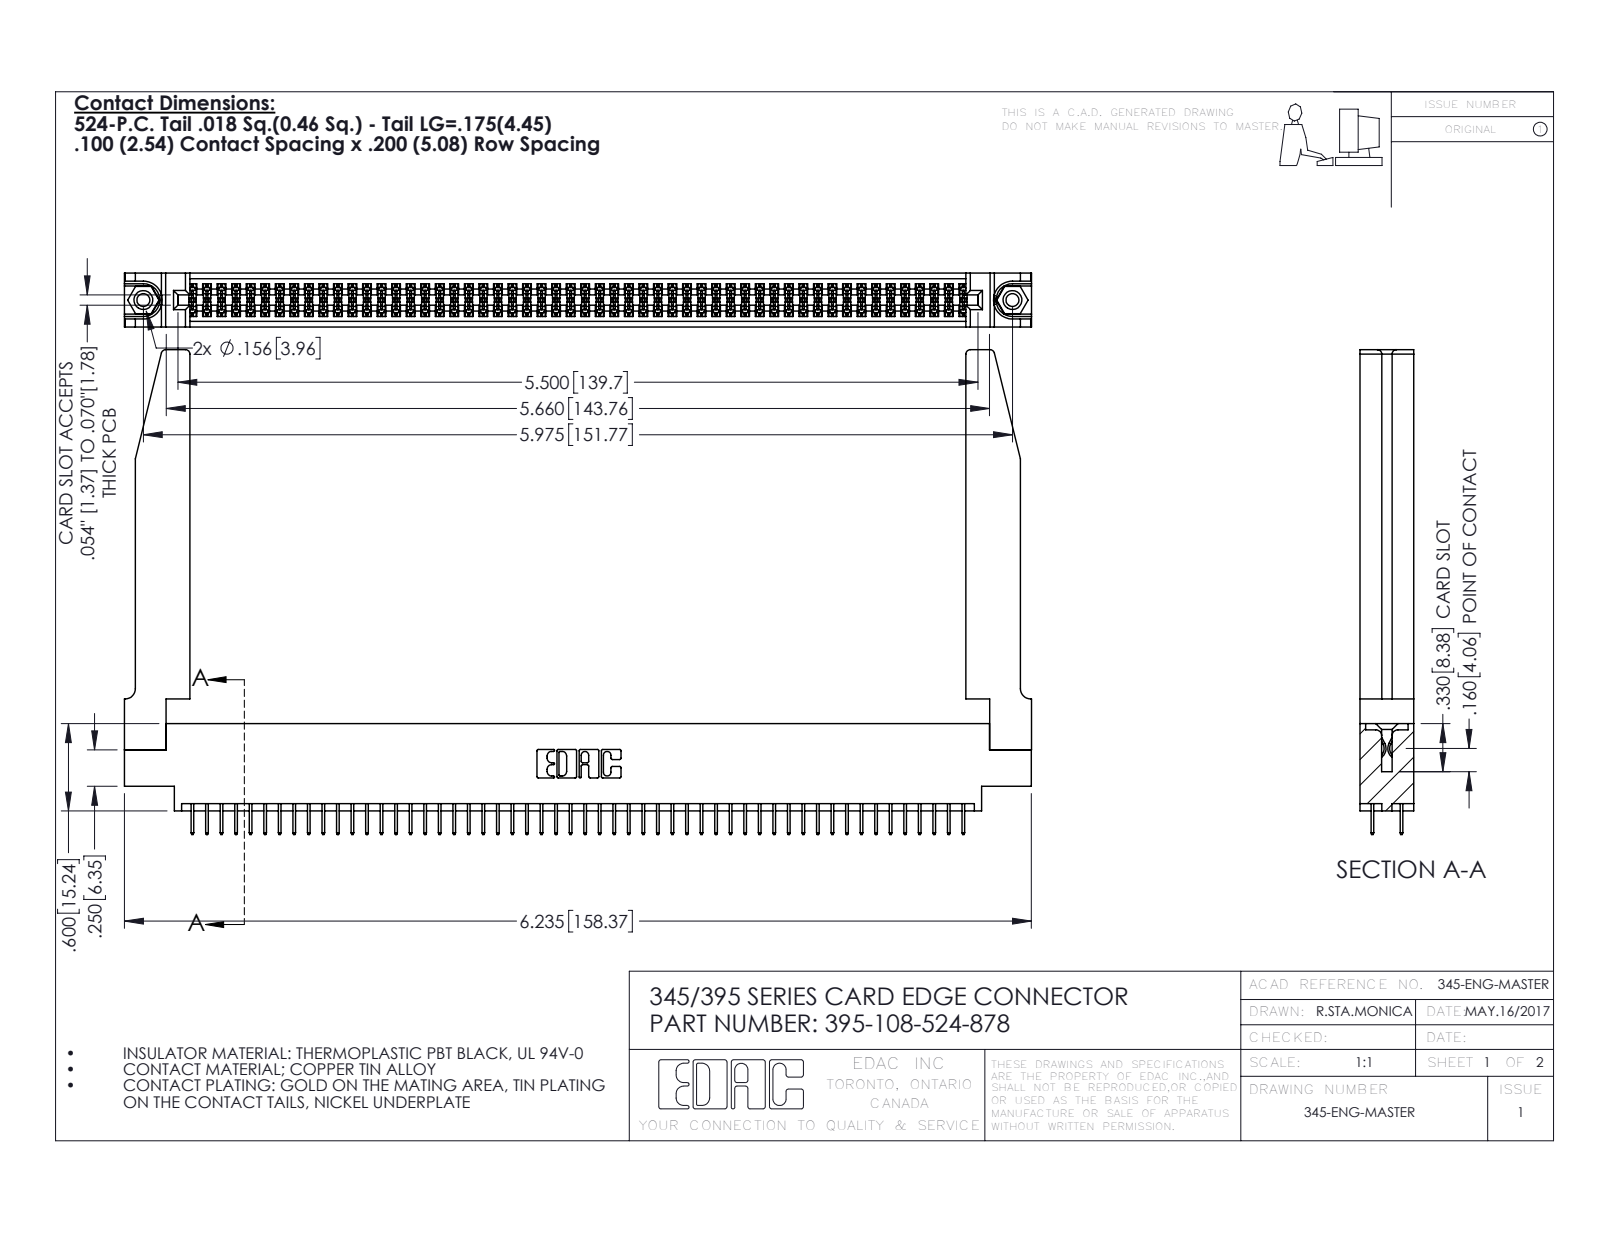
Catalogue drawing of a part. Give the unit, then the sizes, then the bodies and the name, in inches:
Units: inches
Overall size (bounding box): 6.236 × 3.332 × 0.37
Round holes (diameter × count): ⌀0.089 ×2, ⌀0.125 ×2, ⌀0.156 ×2, ⌀0.064 ×1
Round bosses / shafts (diameter × count): ⌀0.155 ×2
Partial cylindrical surfaces — rounded edges, fillets, slot ends (radius × count): R0.006 ×162, R0.01 ×22, R0.03 ×8, R0.007 ×6, R0.031 ×6, R0.026 ×3, R0.014 ×2, R0.019 ×2
Main face-to-face distances: 0.37, 0.072, 0.298, 0.2, 0.098, 0.272, 0.025, 0.225, 0.072, 0.175
Hole centre spacings: 0.27, 5.739, 5.975
Volume: 1.403 in³ · Surface area: 45.39 in²
Bodies: 113 solids, 6196 faces (4438 planar, 1706 cylindrical, 52 other)
Part name (STEP PRODUCT): 345 Part_0.170 Offset - 0.156 Dia-TH; 345-250-001_345-250-001-102; 345-220-078_345-220-078; 345-292-001_345-293-124 (+1 more)
STEP written by: SolidWorks 2016 (CONFIG_CONTROL_DESIGN)
